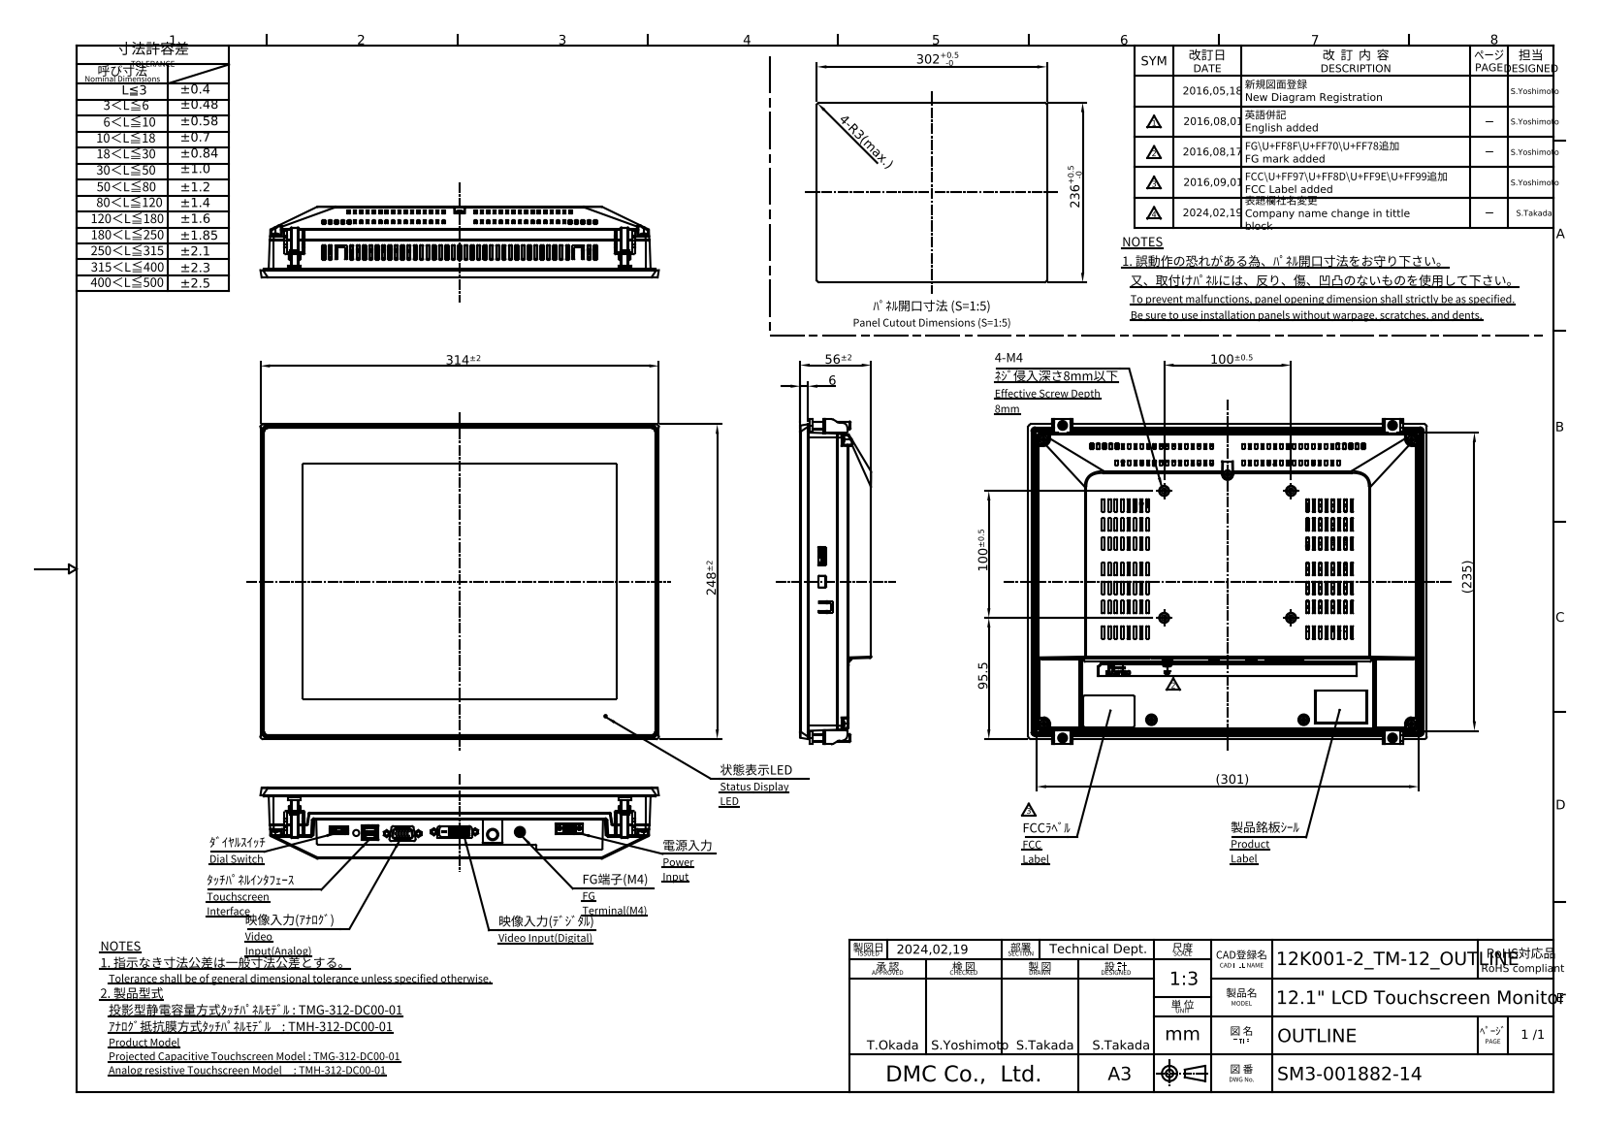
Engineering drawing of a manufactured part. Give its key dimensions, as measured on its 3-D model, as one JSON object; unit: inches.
{"part_name": "HP_TMG-312-DC00-01", "step_written_by": "Autodesk Inventor 2017 (CONFIG_CONTROL_DESIGN)", "units": "inches", "bodies": {"solids": 5, "faces": 7275, "planar": 3975, "cylindrical": 1434, "other": 1866}, "overall_size": [12.362, 10.09, 2.205], "volume_in3": 38.86, "surface_area_in2": 1102, "round_holes": [[0.138, 126], [0.118, 34], [0.315, 27], [0.039, 19], [0.157, 10], [0.126, 7], [0.177, 6], [0.063, 4], [0.098, 4], [0.102, 4], [0.354, 4], [0.189, 3]], "round_bosses_or_shafts": [[0.242, 16], [0.142, 10], [0.244, 8], [0.118, 7], [0.281, 5], [0.276, 5], [0.394, 4], [0.236, 4]], "partial_cylinders_radius": [[0.02, 255], [0.012, 130], [0.039, 127], [0.051, 18], [0.004, 13], [0.031, 13], [0.043, 13], [0.118, 13]], "face_to_face_distances": [0.039, 0.748, 0.791, 0.043, 0.787, 0.831, 0.118, 1.091, 0.276, 1.13], "hole_center_spacings": [0.09, 0.156, 0.197, 0.984, 0.09, 0.18, 0.787, 0.18]}
